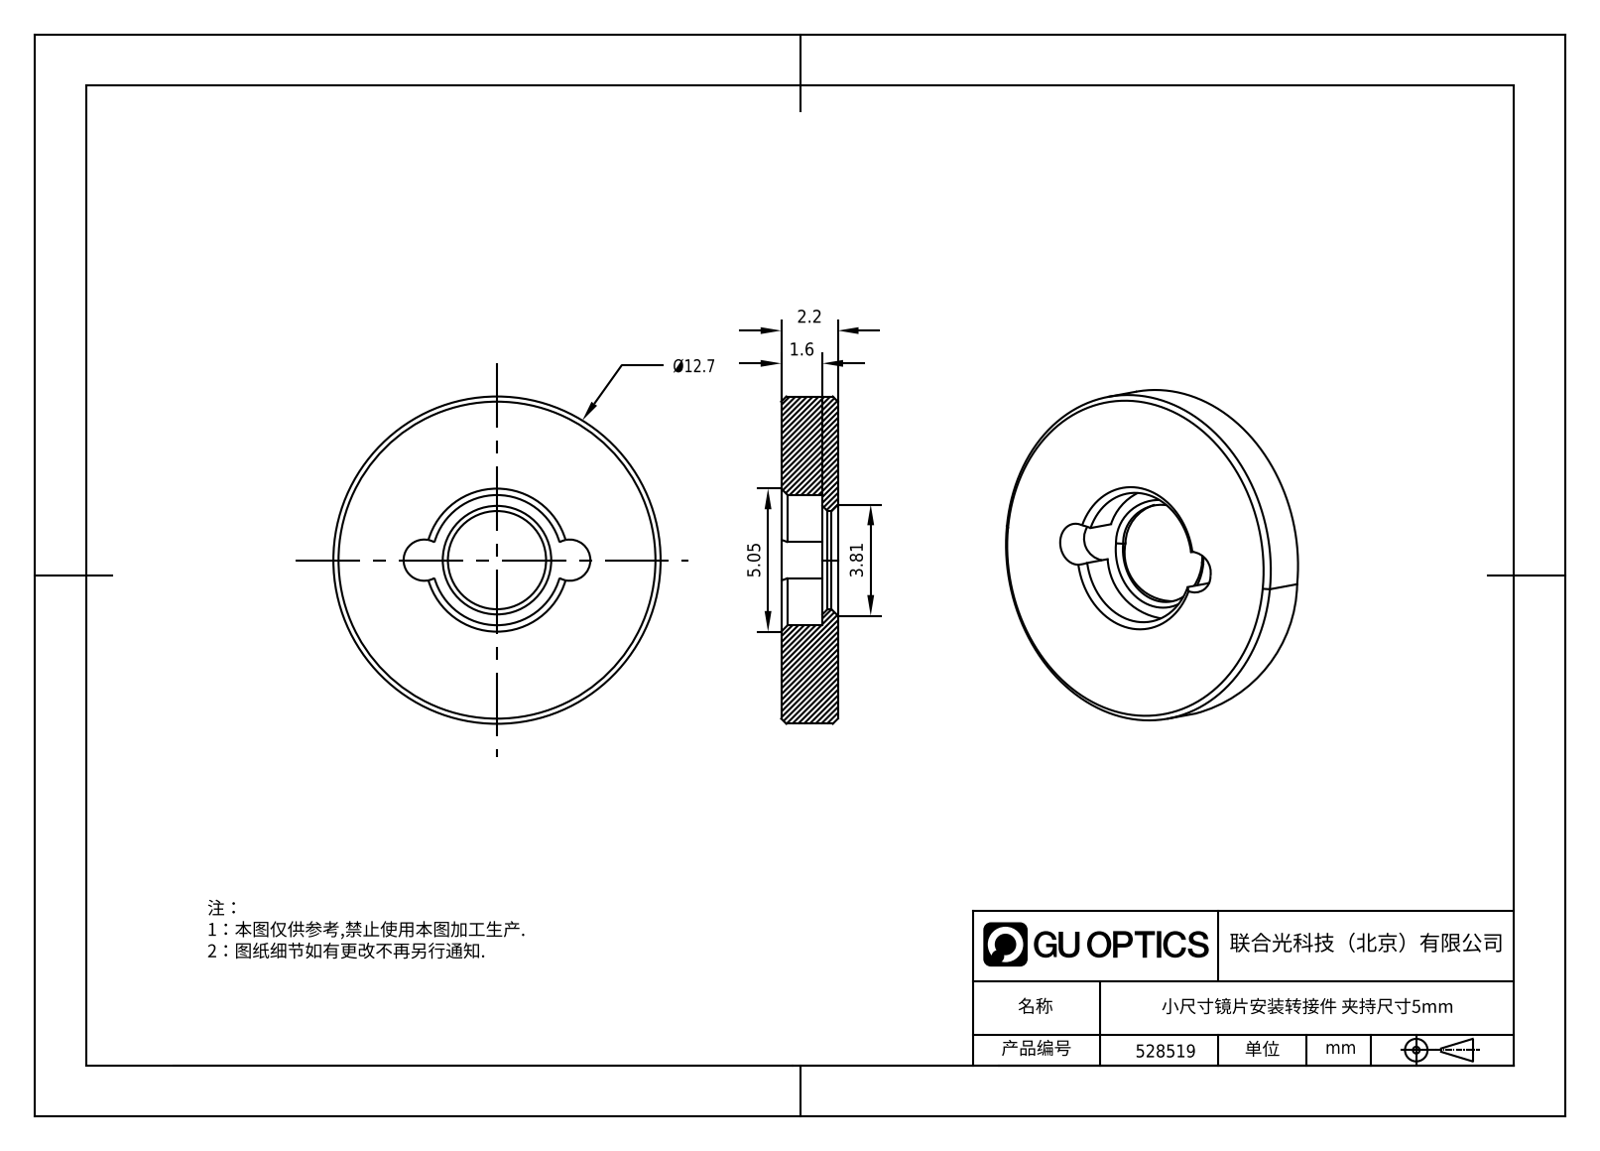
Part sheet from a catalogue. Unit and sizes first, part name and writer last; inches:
Units: inches
Overall size (bounding box): 0.5 × 0.5 × 0.087
Round holes (diameter × count): ⌀0.15 ×1, ⌀0.199 ×1
Round bosses / shafts (diameter × count): ⌀0.5 ×1
Partial cylindrical surfaces — rounded edges, fillets, slot ends (radius × count): R0.031 ×2
Main face-to-face distances: 0.087, 0.024, 0.063
Volume: 0.014 in³ · Surface area: 0.532 in²
Bodies: 1 solid, 22 faces (3 planar, 9 cylindrical, 10 other)
Part name (STEP PRODUCT): 1.6.4.5-ZSJ-05-5
STEP written by: SolidWorks 2021 (CONFIG_CONTROL_DESIGN)
